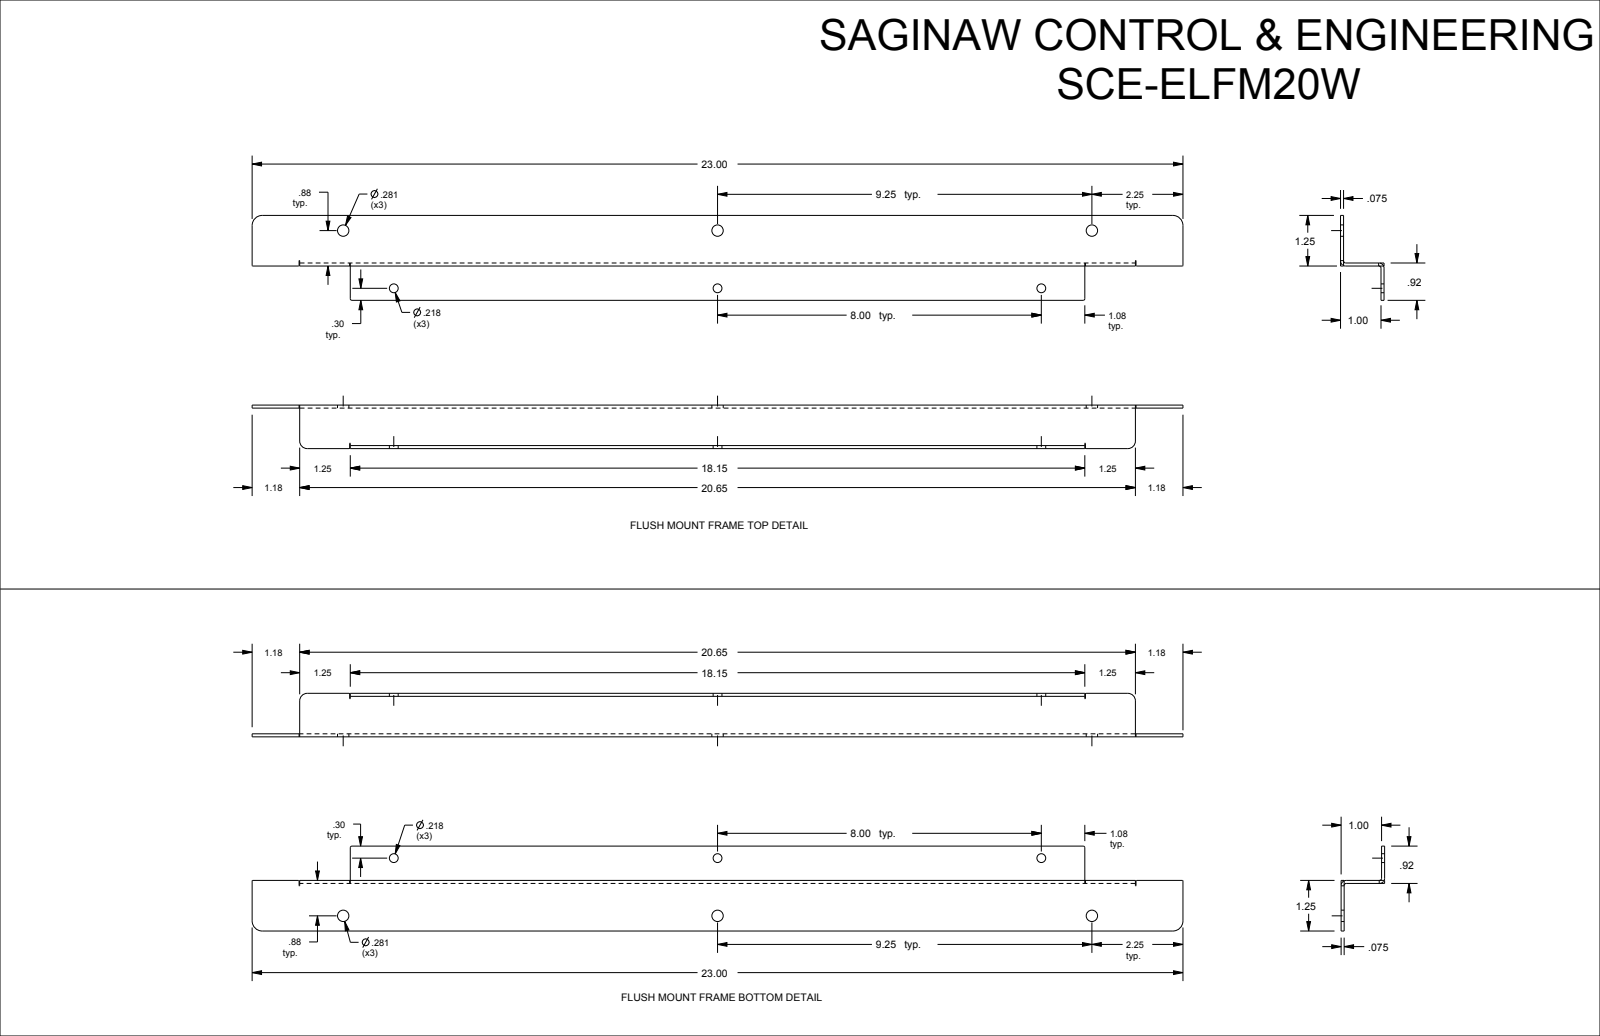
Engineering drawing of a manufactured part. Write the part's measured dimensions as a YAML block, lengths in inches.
part_name: "SCE-ELFM20W"
step_written_by: "SolidWorks 2019 (CONFIG_CONTROL_DESIGN)"
units: inches
bodies: {solids: 2, faces: 96, planar: 44, cylindrical: 52, other: 0}
overall_size: [23, 22.35, 1.075]
volume: 9.443
surface_area: 260.4
round_holes:
  - {diameter: 0.218, count: 6}
  - {diameter: 0.281, count: 6}
partial_cylinders:
  - {radius: 0.015, count: 10}
  - {radius: 0.007, count: 6}
  - {radius: 0.04, count: 4}
  - {radius: 0.051, count: 4}
  - {radius: 0.126, count: 4}
  - {radius: 0.25, count: 4}
  - {radius: 0.187, count: 2}
face_to_face_distances: [0.075, 1, 1.075, 0.925, 19.85, 19.925, 20, 19.925, 0.075, 0.922]
hole_center_spacings: [8, 8.126, 9.25, 9.359, 17.309, 20.385, 23.497, 18.75]
